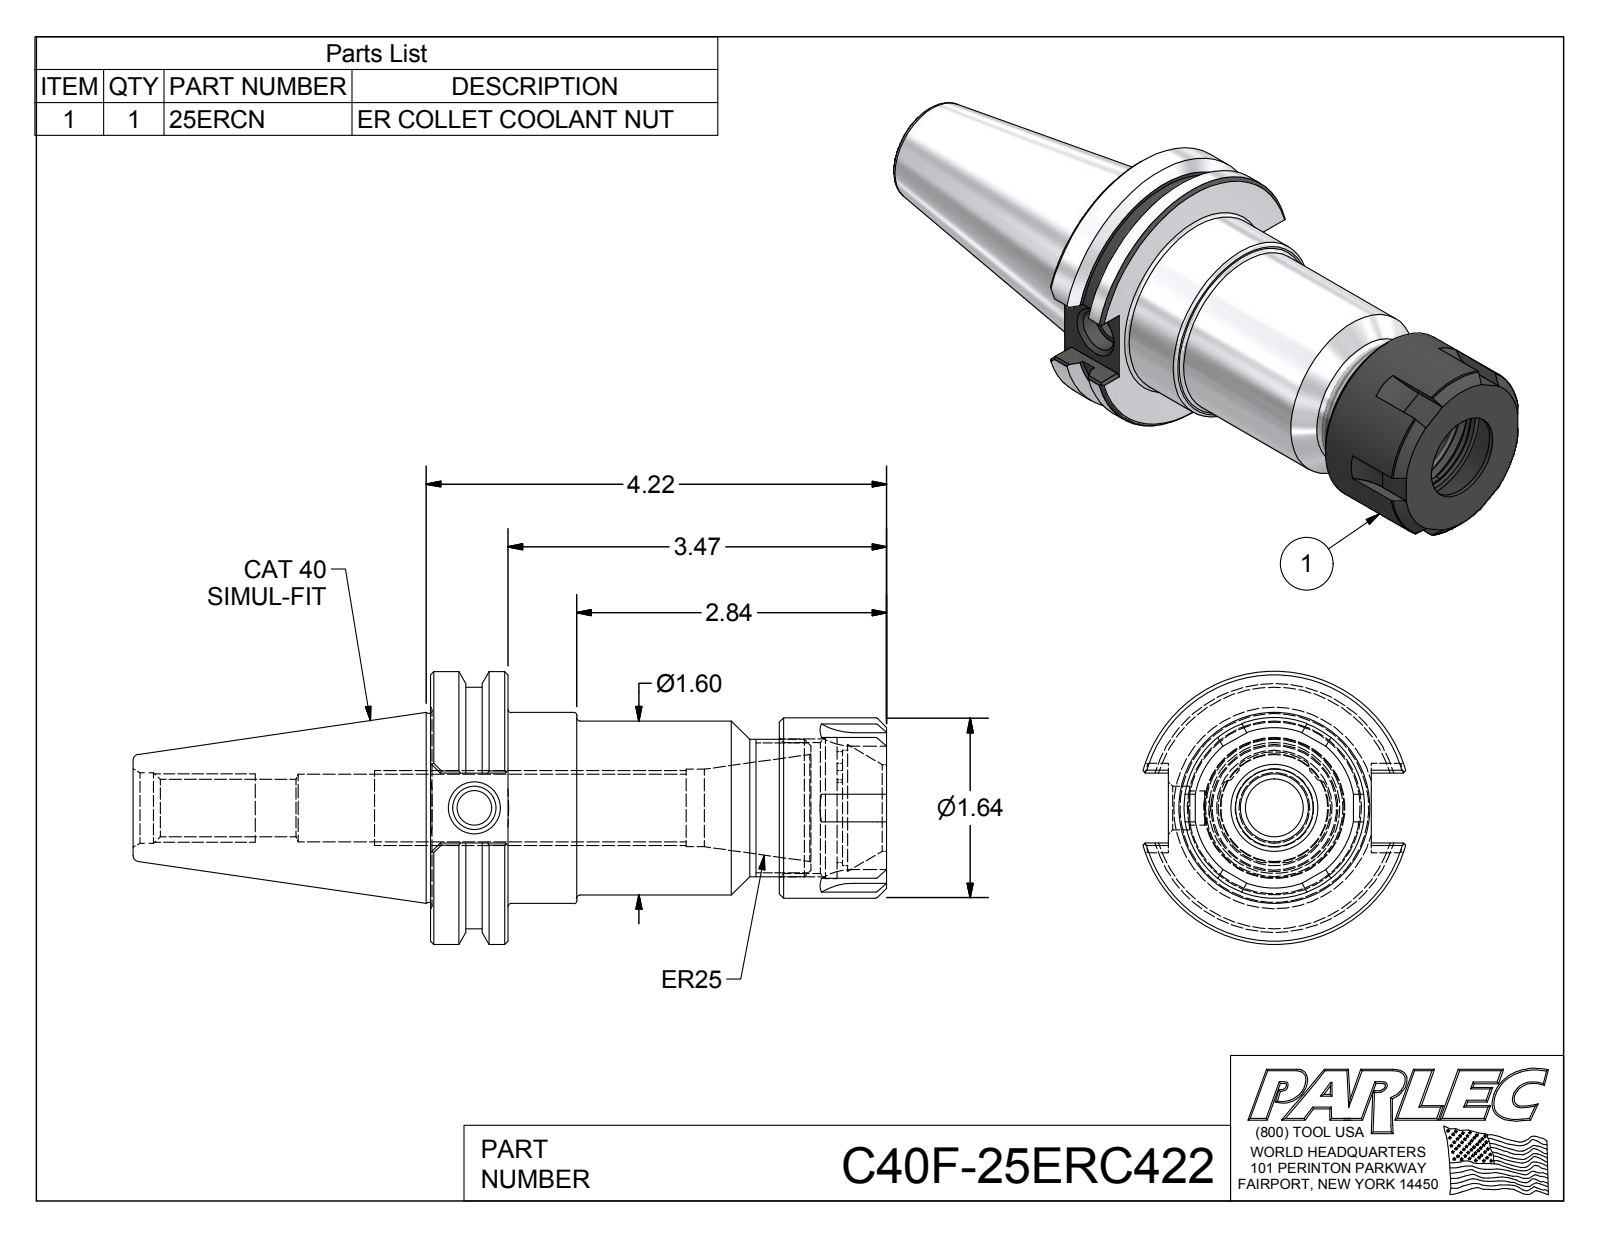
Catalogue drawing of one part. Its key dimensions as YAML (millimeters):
part_name: "C40F-25ERC422; C40F-25ER4-1; 25ERCN"
step_written_by: "Autodesk Inventor 2018 (AUTOMOTIVE_DESIGN)"
units: millimeters
bodies: {solids: 2, faces: 137, planar: 61, cylindrical: 31, other: 45}
overall_size: [175.5, 63.5, 61.1]
volume: 186500
surface_area: 40590
round_holes:
  - {diameter: 8, count: 1}
  - {diameter: 10.1, count: 1}
  - {diameter: 13.4, count: 1}
  - {diameter: 15.7, count: 1}
  - {diameter: 16.5, count: 1}
  - {diameter: 18, count: 1}
  - {diameter: 20.2, count: 1}
  - {diameter: 26.8, count: 1}
  - {diameter: 30.5, count: 1}
  - {diameter: 32.9, count: 1}
round_bosses_or_shafts:
  - {diameter: 63.5, count: 1}
  - {diameter: 56.3, count: 1}
  - {diameter: 44.5, count: 1}
  - {diameter: 42, count: 1}
  - {diameter: 40.5, count: 1}
  - {diameter: 32, count: 1}
partial_cylinders:
  - {radius: 12.7, count: 6}
  - {radius: 12, count: 1}
  - {radius: 13.1, count: 1}
face_to_face_distances: [18, 106.2, 88.1, 81.2, 63.1, 25, 94.7, 76.6, 13.5, 11.5]
